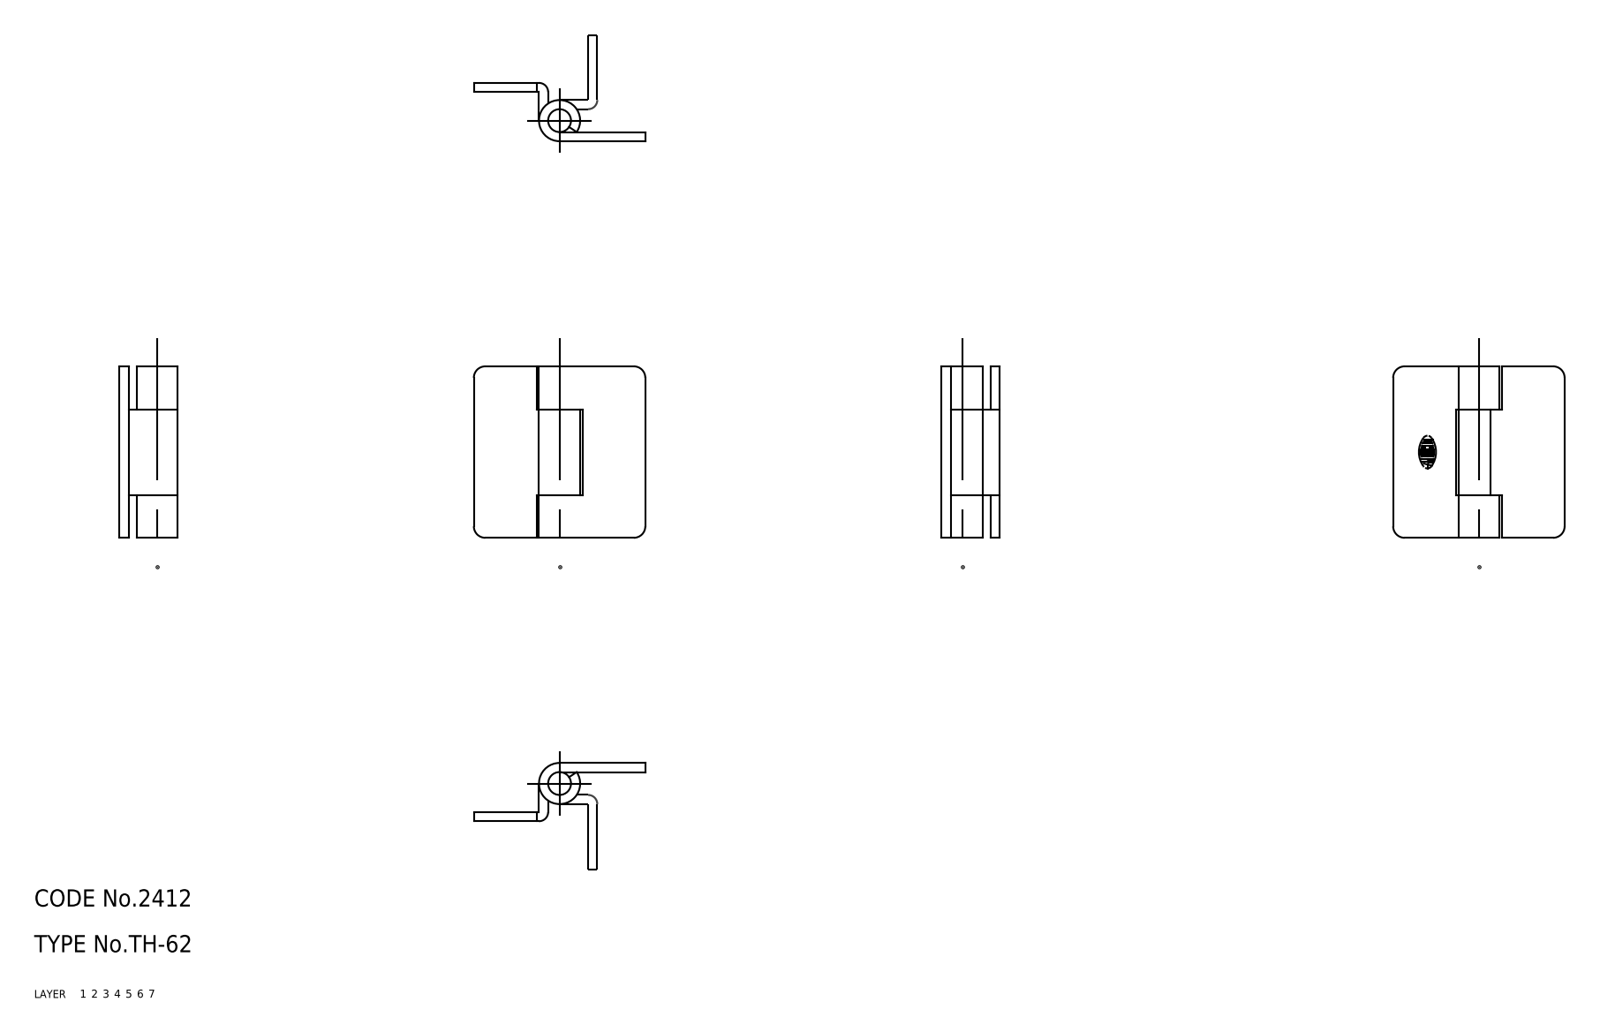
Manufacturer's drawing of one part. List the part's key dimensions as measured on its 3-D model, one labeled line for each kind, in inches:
Part name (STEP PRODUCT): shaft; hinge piece_B; hinge piece_A; TH_62_13023_36
STEP written by: CADfix (AUTOMOTIVE_DESIGN)
Units: inches
Bodies: 3 solids, 37 faces (0 planar, 0 cylindrical, 37 other)
Overall size (bounding box): 1.181 × 1.181 × 0.402
Volume: 0.146 in³ · Surface area: 5.222 in²
